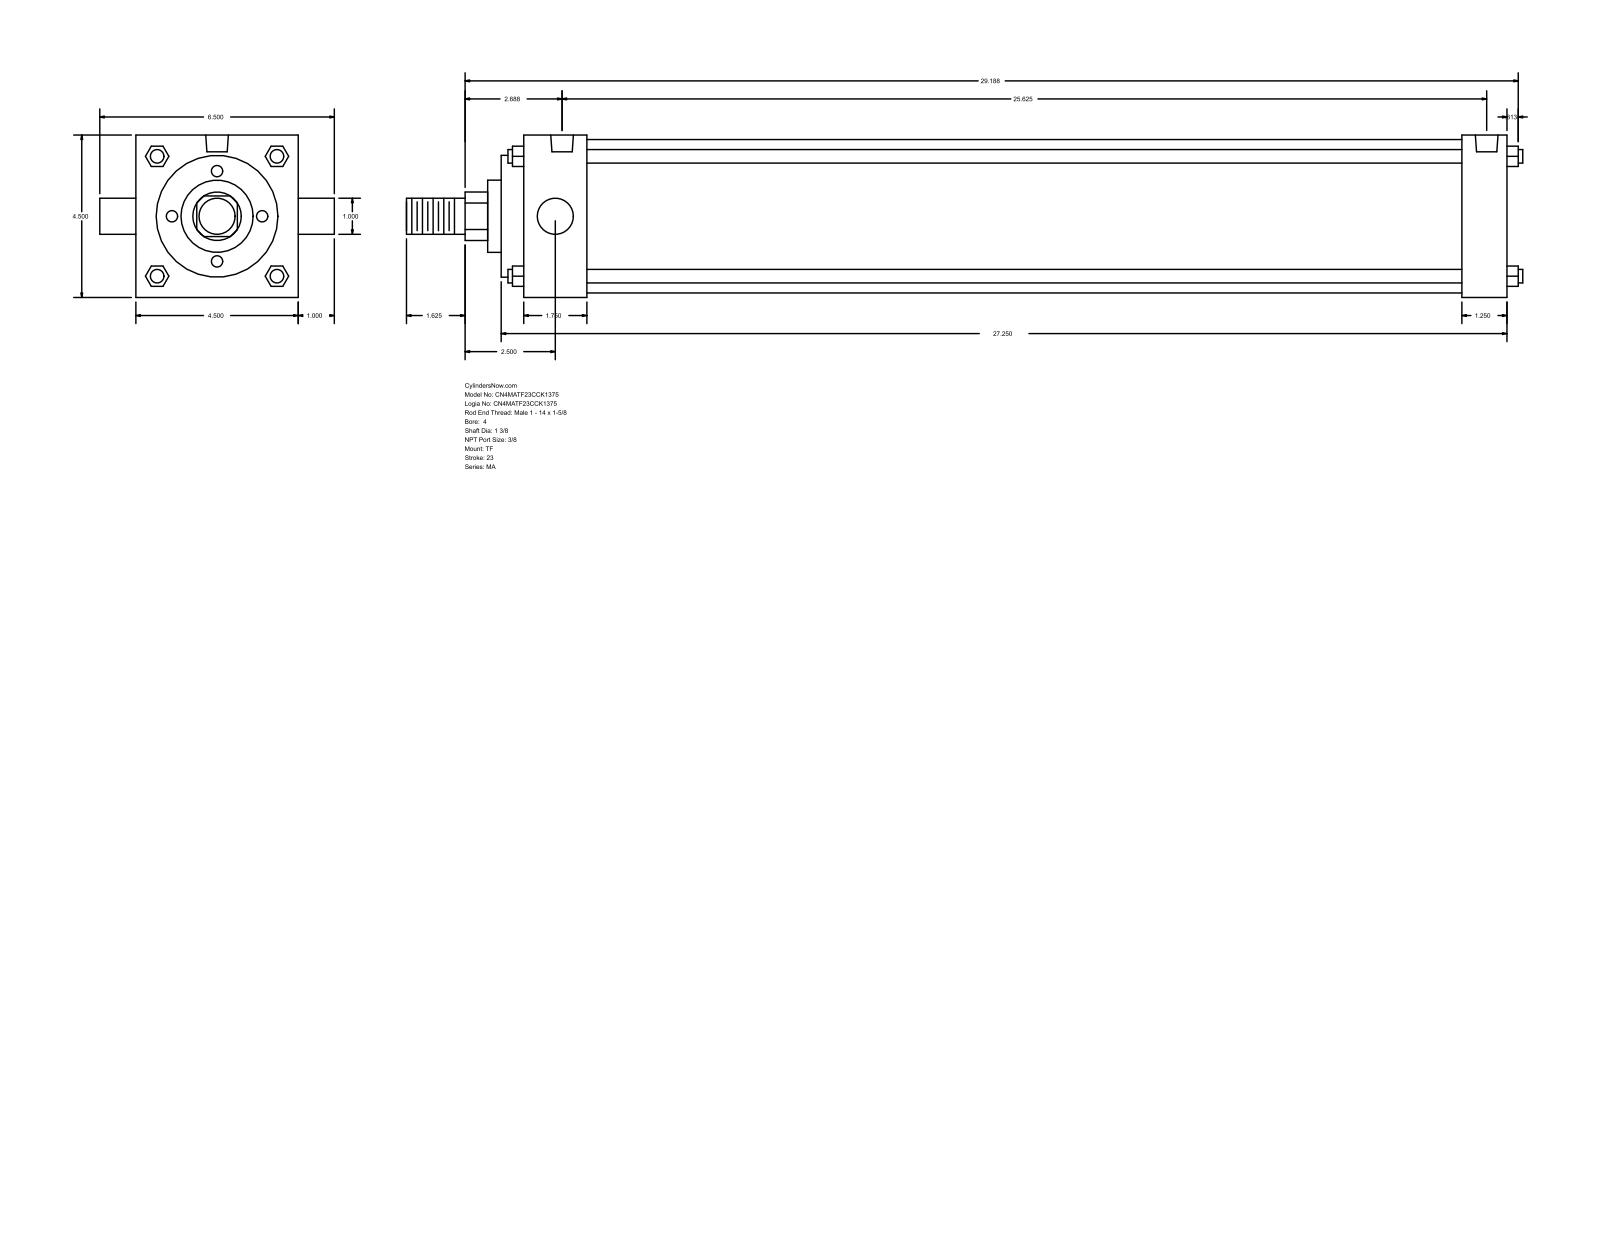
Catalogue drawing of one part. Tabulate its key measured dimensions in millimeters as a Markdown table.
| quantity | value |
| --- | --- |
| part name | MA_TF__0400_1.375 |
| STEP written by | GSSL Pune (CONFIG_CONTROL_DESIGN) |
| units | millimeters |
| bodies | 0 solids, 122 faces (93 planar, 29 cylindrical, 0 other) |
| overall size | 785.81 × 165.1 × 114.3 |
| round holes (diameter × count) | 11.11 × 3, 15.93 × 2 |
| round bosses / shafts (diameter × count) | 9.53 × 4, 25.4 × 2, 107.95 × 1, 85.72 × 1, 50.8 × 1, 34.92 × 1 |
| partial cylindrical surfaces (radius × count) | 17.06 × 1 |
| main face-to-face distances | 114.3, 692.15, 708.02, 15.87, 676.27, 660.4, 31.75, 60.32, 44.45, 615.95 |
| hole center spacings | 4.76, 4.77, 641.35, 646.11, 646.12, 650.88 |
